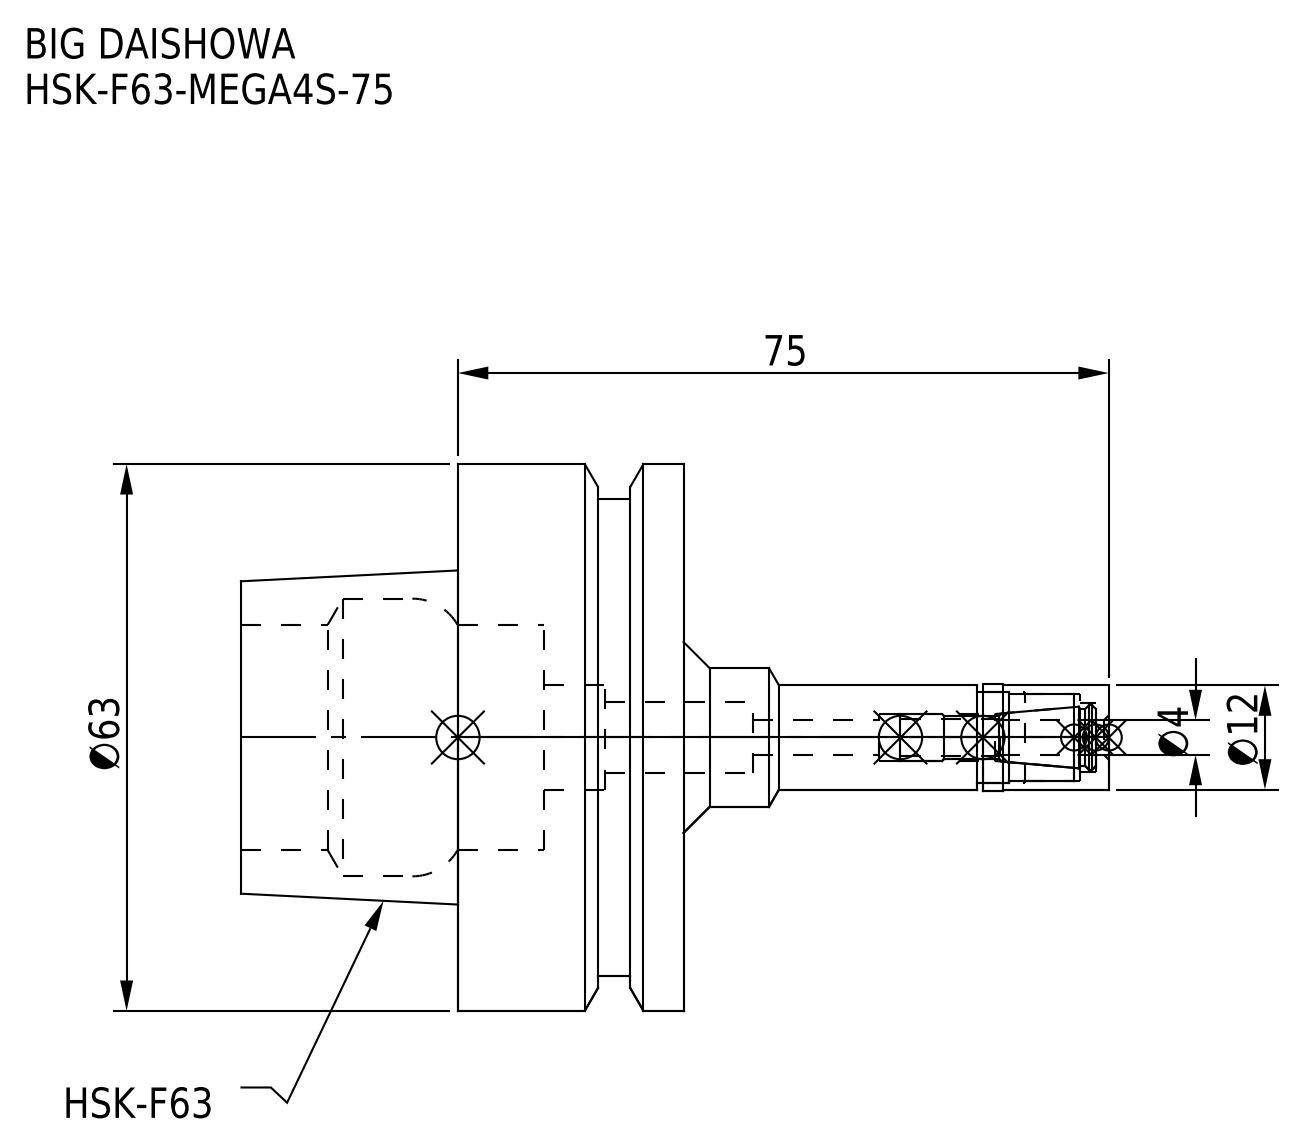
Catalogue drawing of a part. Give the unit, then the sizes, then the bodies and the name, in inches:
Units: inches
Overall size (bounding box): 3.937 × 2.48 × 2.48
Round holes (diameter × count): ⌀0.161 ×1, ⌀0.213 ×1, ⌀0.315 ×1, ⌀0.325 ×1, ⌀0.394 ×1, ⌀0.413 ×1, ⌀1.024 ×1, ⌀1.26 ×1
Round bosses / shafts (diameter × count): ⌀2.48 ×1, ⌀2.165 ×1, ⌀0.63 ×1, ⌀0.484 ×1, ⌀0.472 ×1
Main face-to-face distances: 1.024, 0.984, 2.008, 0.632, 0.392, 1.376, 0.241, 0.391, 0.783, 1.767
Volume: 5.3 in³ · Surface area: 34.94 in²
Bodies: 2 solids, 78 faces (18 planar, 42 cylindrical, 18 other)
Part name (STEP PRODUCT): HSK-F63-MEGA4S-75_1.stp; DXF_TEMP_ASSY_ASM_4_ASM.stp; MGN4S_1.stp; HF63MS04075-040_ASM.stp (+3 more)
STEP written by: SolidWorks 2019 (CONFIG_CONTROL_DESIGN)
